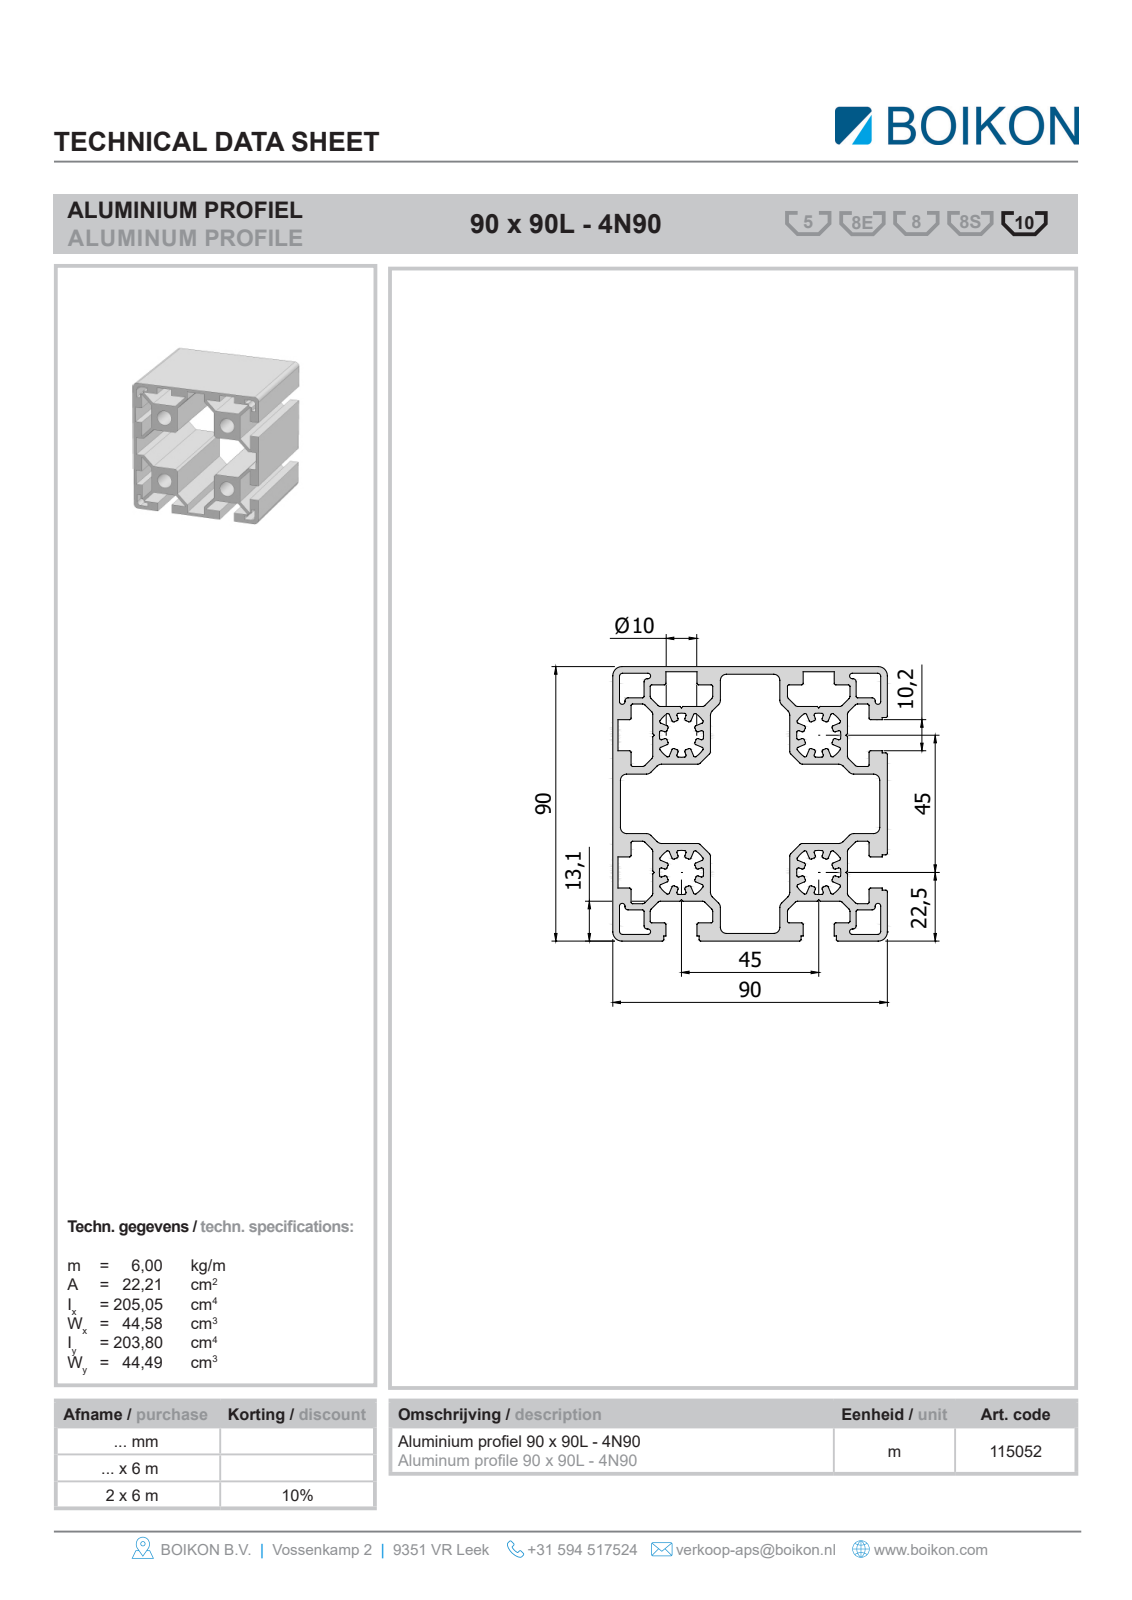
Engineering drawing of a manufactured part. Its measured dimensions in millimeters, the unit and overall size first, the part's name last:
Units: millimetres
Overall size (bounding box): 1000 × 90 × 90
Round holes (diameter × count): ⌀10.2 ×4
Partial cylindrical surfaces — rounded edges, fillets, slot ends (radius × count): R2.5 ×4, R3 ×4
Main face-to-face distances: 45, 7.1, 25.9, 2, 6, 84, 13.1, 76.9, 70.9, 31.9
Hole centre spacings: 45, 63.64
Volume: 2 580 000 mm³ · Surface area: 1 438 000 mm²
Bodies: 1 solid, 142 faces (126 planar, 16 cylindrical, 0 other)
Part name (STEP PRODUCT): Root; 11505290x90L-4N90BOIKON0
STEP written by: HiCAD 2013 1802.4 Build 509 (AUTOMOTIVE_DESIGN)
